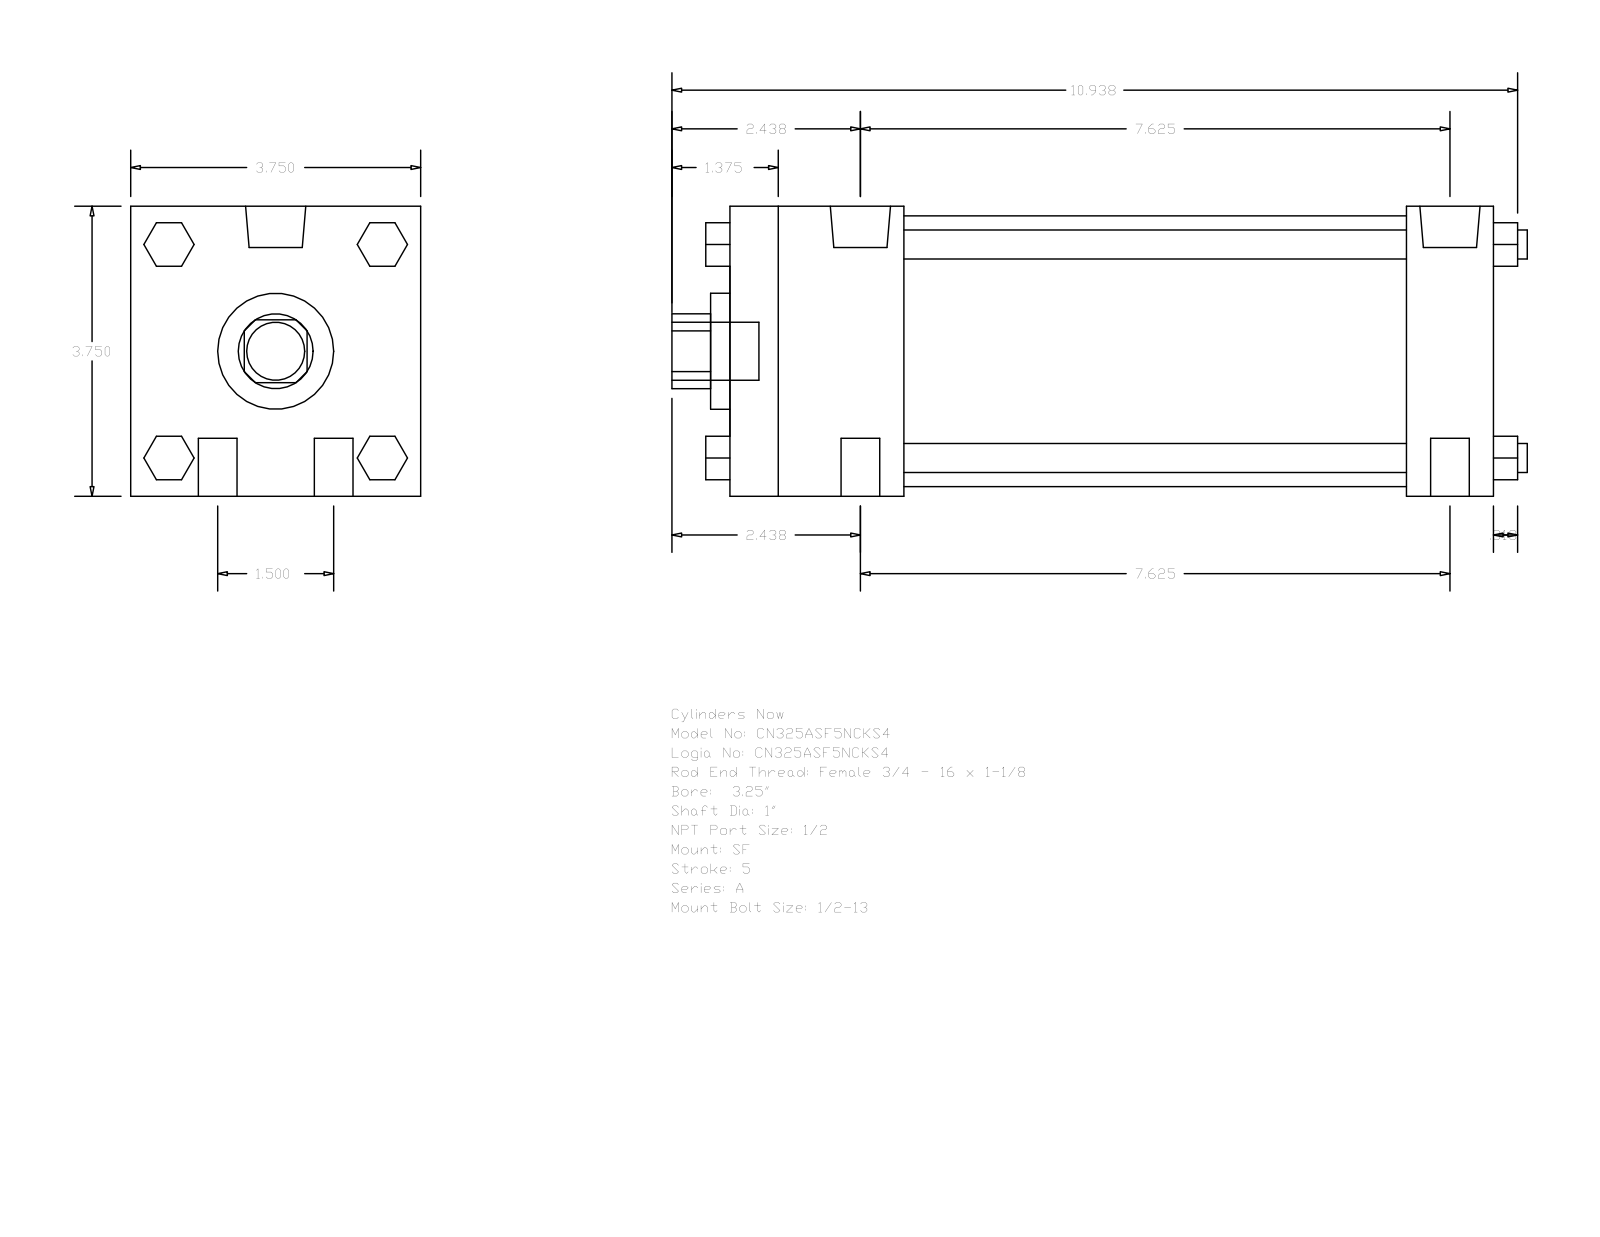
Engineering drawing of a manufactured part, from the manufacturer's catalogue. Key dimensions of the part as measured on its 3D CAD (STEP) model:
Part name (STEP PRODUCT): A_SF__0325_1
STEP written by: GSSL Pune (CONFIG_CONTROL_DESIGN)
Units: millimetres
Bodies: 0 solids, 124 faces (94 planar, 30 cylindrical, 0 other)
Overall size (bounding box): 280.99 × 95.25 × 95.25
Round holes (diameter × count): ⌀25.4 ×1, ⌀38.1 ×1, ⌀88.9 ×1
Round bosses / shafts (diameter × count): ⌀12.7 ×4, ⌀9.53 ×4, ⌀19.77 ×2, ⌀8.73 ×2, ⌀19.05 ×1
Partial cylindrical surfaces — rounded edges, fillets, slot ends (radius × count): R12.29 ×1
Main face-to-face distances: 95.24, 250.83, 222.25, 28.58, 57.15, 165.1, 193.68, 14.28, 35.05, 60.71
